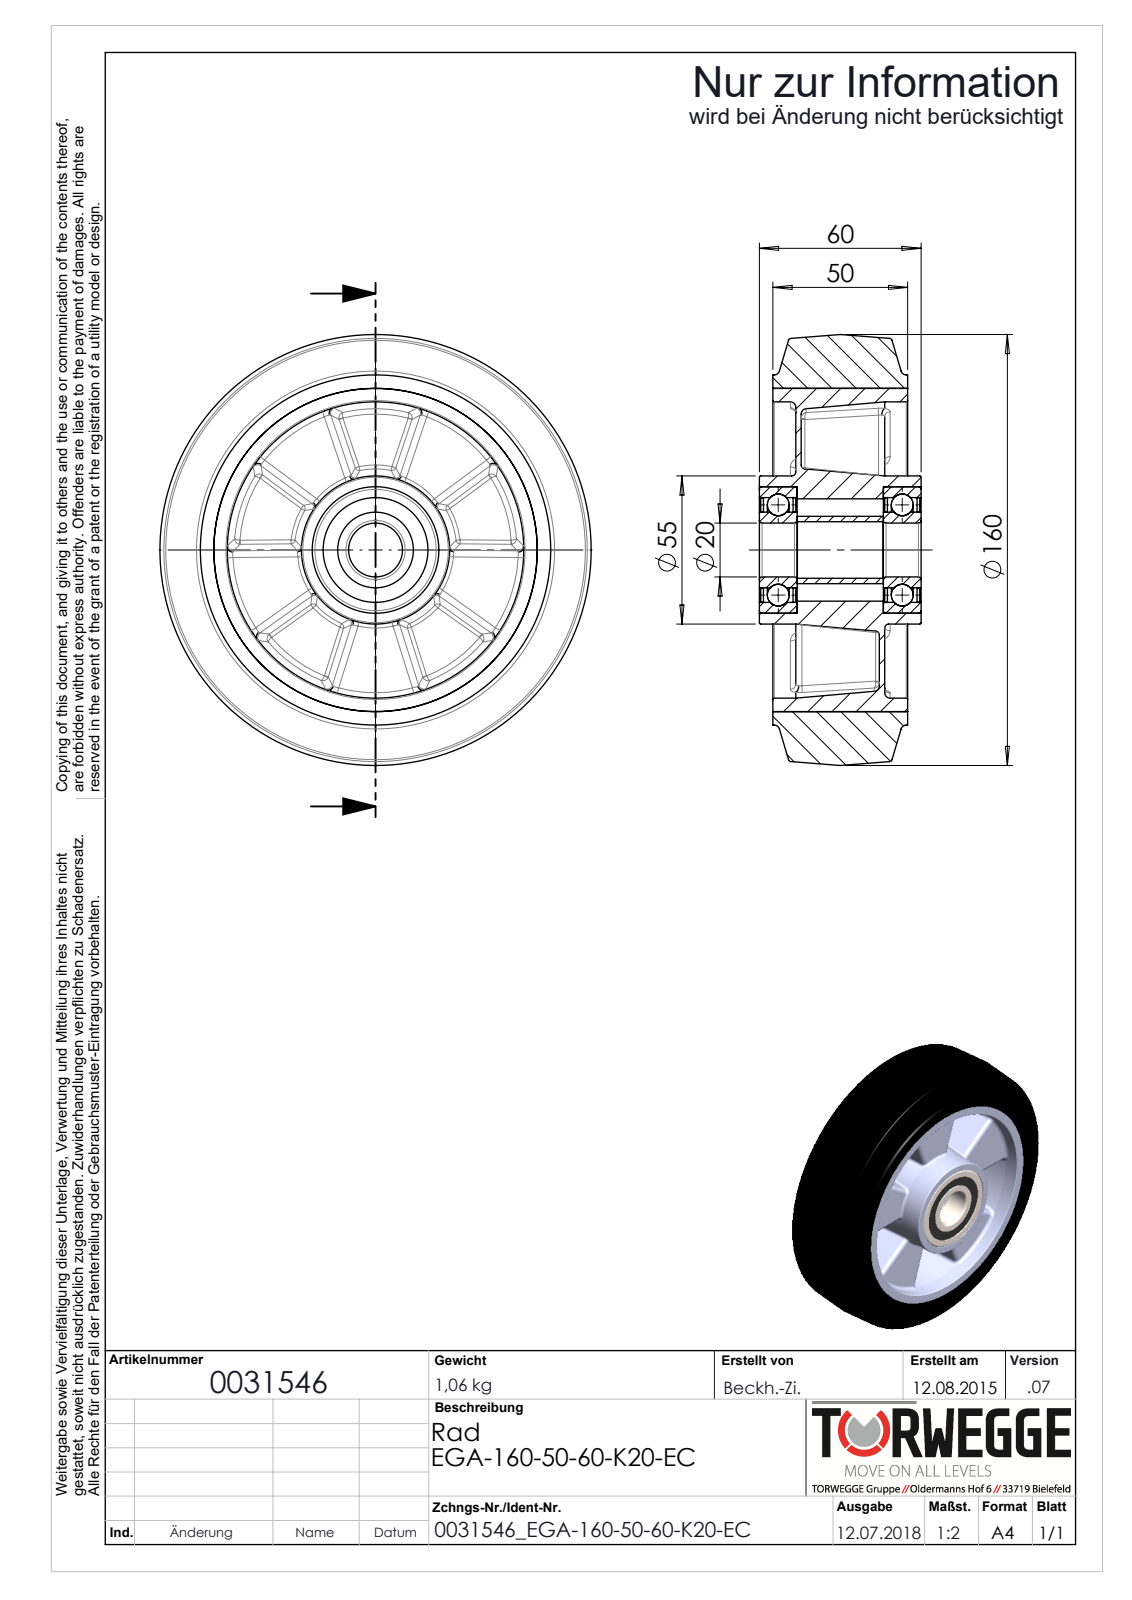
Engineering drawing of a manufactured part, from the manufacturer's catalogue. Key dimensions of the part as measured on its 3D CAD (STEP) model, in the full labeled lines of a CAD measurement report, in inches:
Part name (STEP PRODUCT): 0031546_EGA-160-50-60-K20-EC
STEP written by: SolidWorks 2016 (AUTOMOTIVE_DESIGN)
Units: inches
Bodies: 9 solids, 475 faces (66 planar, 106 cylindrical, 303 other)
Overall size (bounding box): 6.299 × 6.299 × 2.362
Volume: 37.32 in³ · Surface area: 252.9 in²
Round holes (diameter × count): ⌀0.787 ×1, ⌀0.827 ×1, ⌀1.106 ×1, ⌀1.496 ×1, ⌀1.531 ×1, ⌀1.85 ×1, ⌀4.331 ×1, ⌀4.724 ×1
Round bosses / shafts (diameter × count): ⌀5.118 ×1, ⌀2.165 ×1, ⌀0.984 ×1
Partial cylindrical surfaces — rounded edges, fillets, slot ends (radius × count): R0.059 ×20, R0.098 ×20
Main face-to-face distances: 0.335, 1.634, 0.059, 1.811, 0.02, 1.969, 0.531, 0.551, 1.752, 0.113
